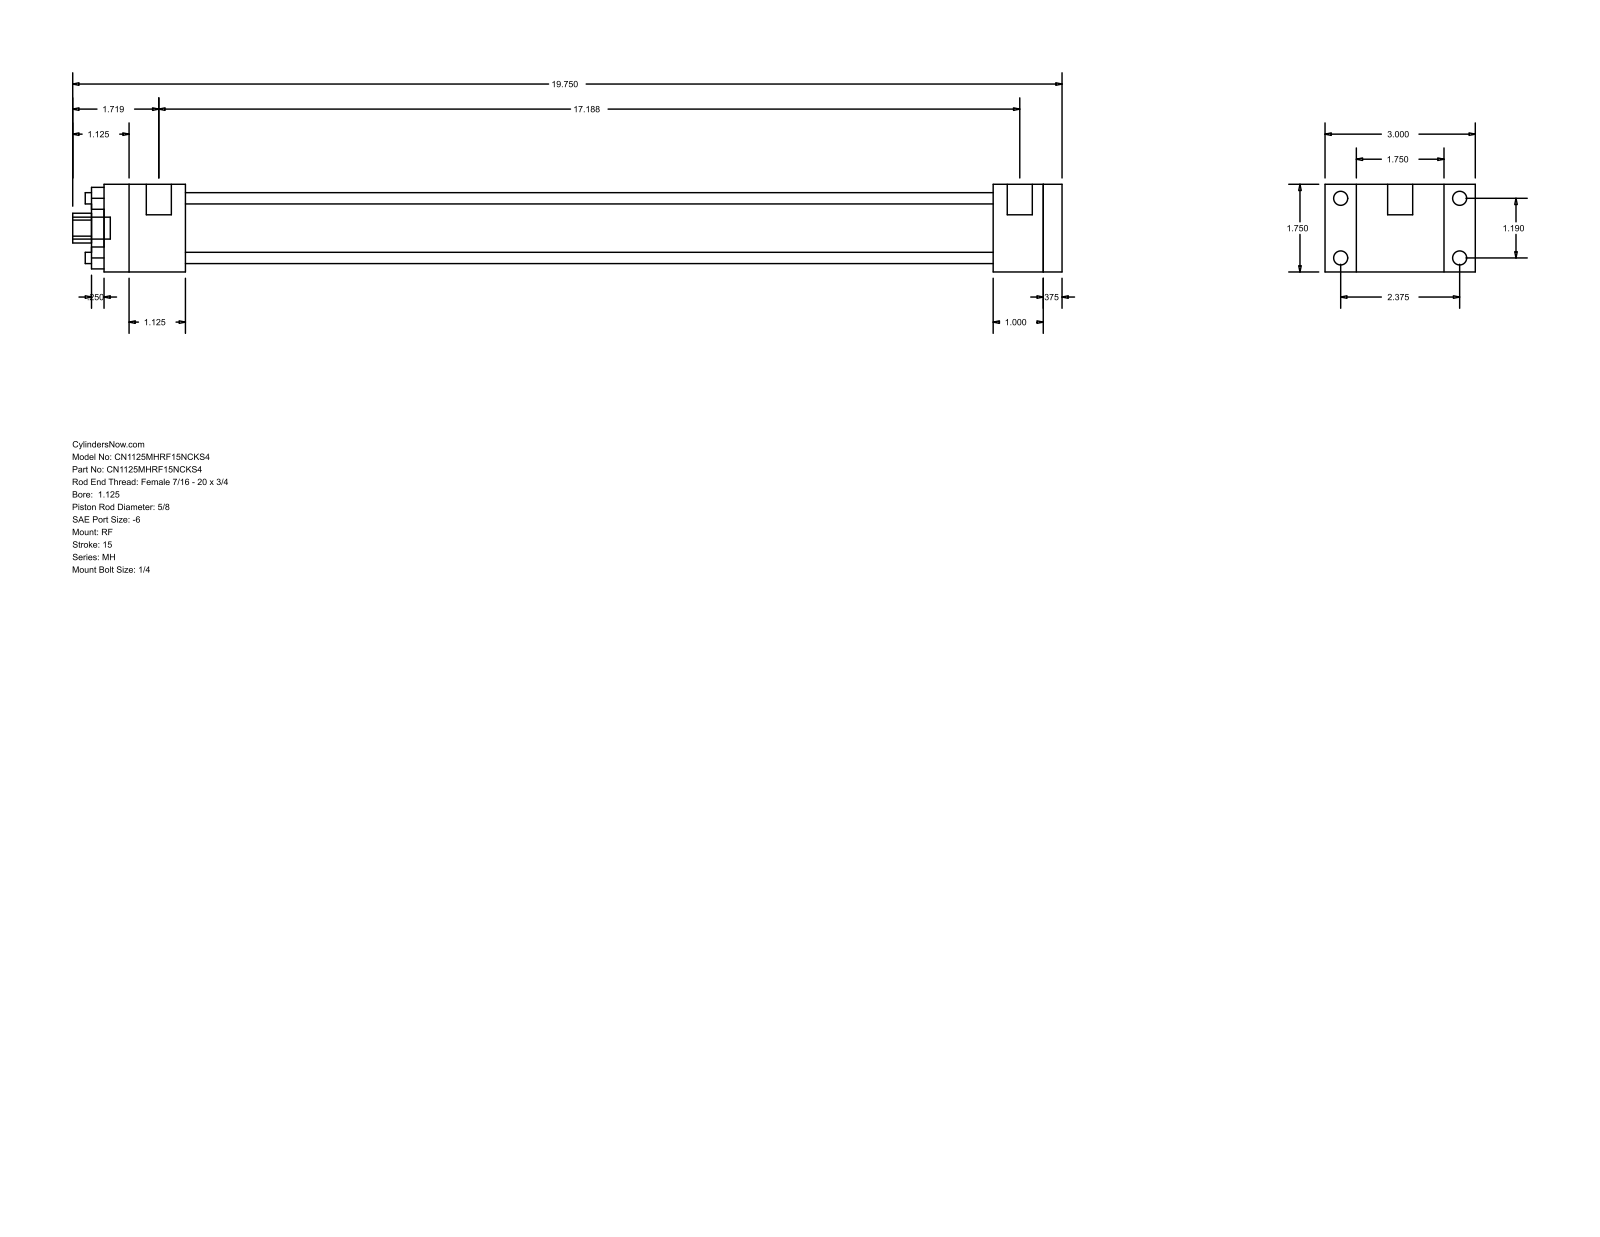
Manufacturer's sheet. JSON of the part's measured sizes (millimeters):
{"part_name": "MH_RF__0112_0.625", "step_written_by": "GSSL Pune (CONFIG_CONTROL_DESIGN)", "units": "millimeters", "bodies": {"solids": 0, "faces": 92, "planar": 64, "cylindrical": 28, "other": 0}, "overall_size": [501.65, 76.2, 44.45], "round_holes": [[5.71, 4], [15.88, 1], [28.57, 1], [34.92, 1]], "round_bosses_or_shafts": [[7.14, 4], [5.56, 4], [12.7, 2], [11.11, 1]], "partial_cylinders_radius": [[7.54, 1]], "face_to_face_distances": [44.46, 9.53, 485.77, 15.87, 434.97, 444.5, 409.58, 25.39, 34.92, 41.27], "hole_center_spacings": [21.37, 30.22, 42.74]}
